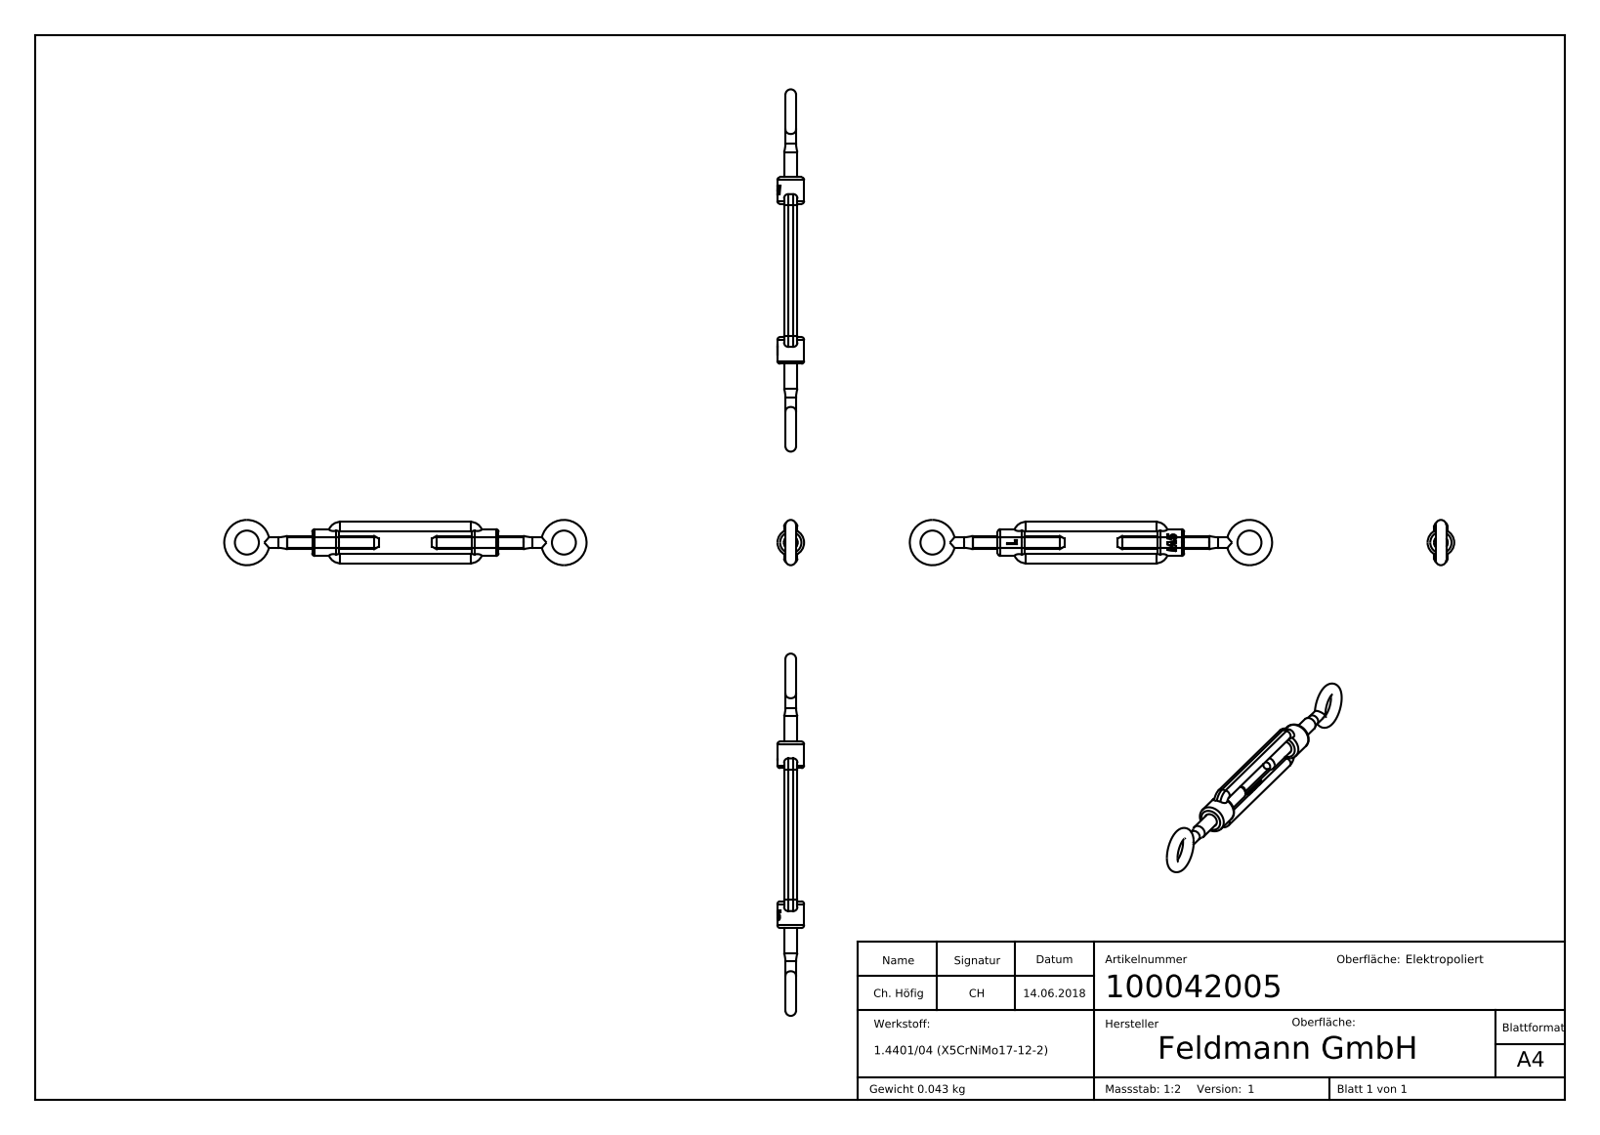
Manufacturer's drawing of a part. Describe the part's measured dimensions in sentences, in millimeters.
The part is named "10004200X Teil2_100042005 Teil2; 100042005; 10004200X Teil1_100042005 Teil1; 10004200X Teil3_100042005 Teil3". Its 3-D file was written by "SolidWorks 2015 (CONFIG_CONTROL_DESIGN)". It is 3 solids with 333 faces: 136 planar, 31 cylindrical and 166 other. Overall it measures 136 by 17 by 10 millimeters. Its volume is 5 422 cubic millimeters and its surface area 4 838 square millimeters. Round holes: 1 of diameter 4.2. Round bosses or shafts: 1 of diameter 10, 1 of diameter 5, 1 of diameter 4. Partial cylindrical surfaces (rounded edges, fillets, slot ends): 4 of radius 1, 4 of radius 1.75, 4 of radius 4.5, 1 of radius 4.98. The main face-to-face distances are 3.5, 12, 15.5, 8.5, 10, 60, 50, 70, 25, 45.
